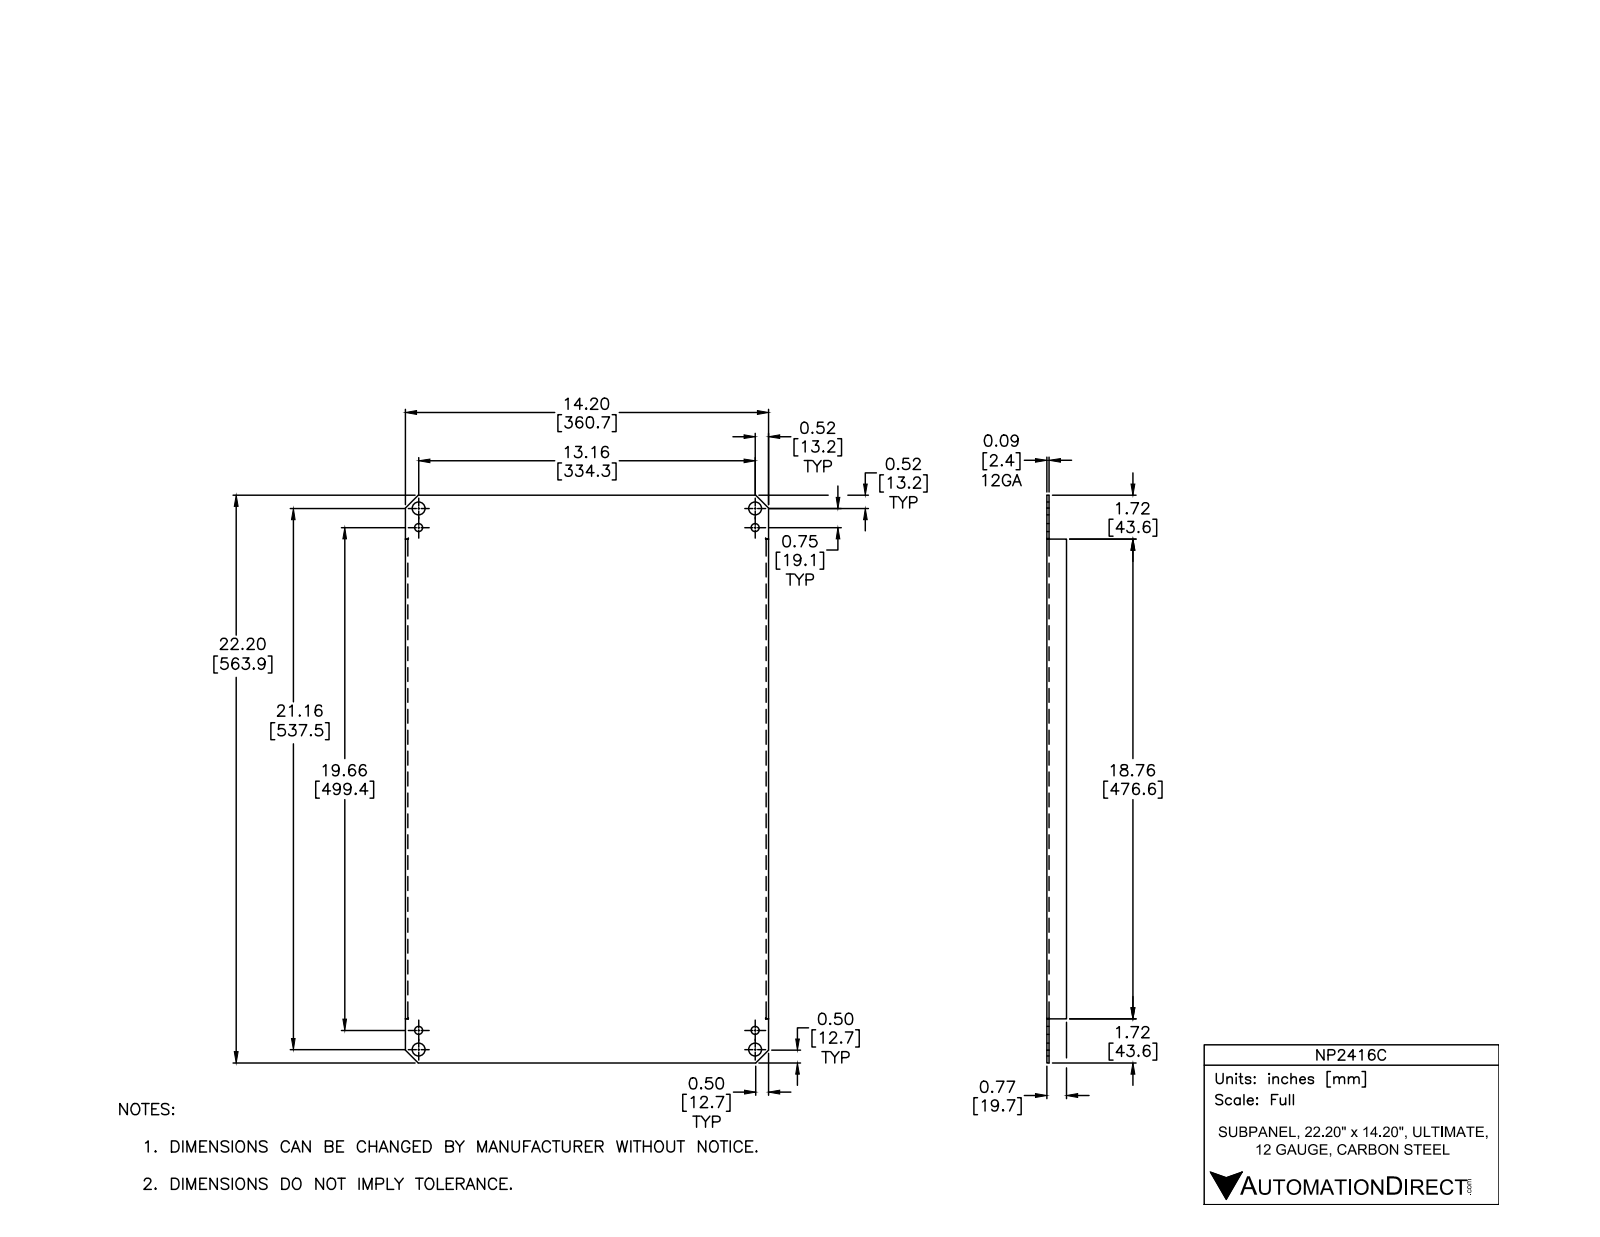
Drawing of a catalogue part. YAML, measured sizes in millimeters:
part_name: "NP2416C"
step_written_by: "Autodesk Inventor 2012 (AUTOMOTIVE_DESIGN)"
units: millimeters
bodies: {solids: 1, faces: 42, planar: 30, cylindrical: 12, other: 0}
overall_size: [563.9, 360.7, 19.7]
volume: 519500
surface_area: 441500
round_holes:
  - {diameter: 8, count: 4}
  - {diameter: 12.7, count: 4}
partial_cylinders:
  - {radius: 0.4, count: 2}
  - {radius: 2.8, count: 2}
face_to_face_distances: [2.4, 358.3, 360.7, 355.9, 17.3, 19.7, 563.9, 43.6, 520.2, 476.6]
hole_center_spacings: [19.1, 334.3, 334.8, 518.4, 616.8, 499.4, 537.5, 600.9]
